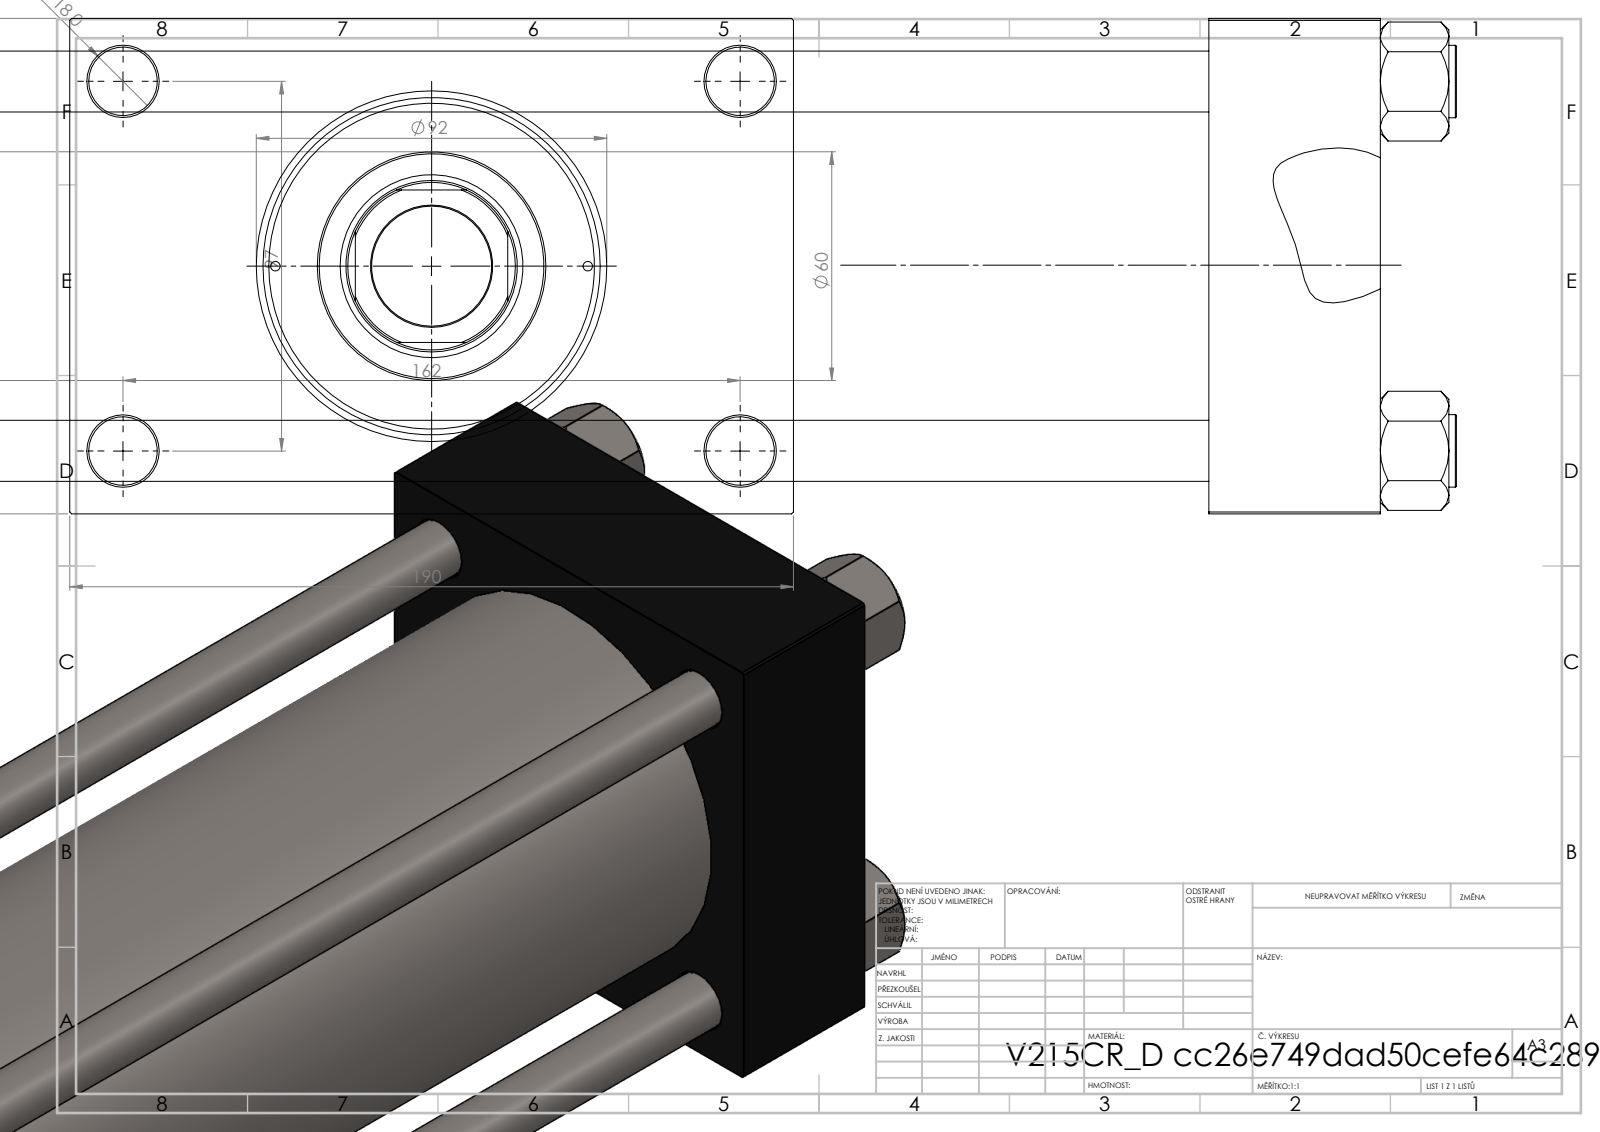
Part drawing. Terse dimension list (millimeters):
name: NUT_M5_D; V215CR_VCP_D; V215CR_D_TYCINKA; V215CR_D_Body (+1 more)
written by: SolidWorks 2019 (CONFIG_CONTROL_DESIGN)
unit: mm
bodies: 11 solids, 1159 faces (547 planar, 92 cylindrical, 520 other)
size: 523 × 190 × 130
volume: 3 532 000 mm³; area: 631 811 mm²
holes: 4× ⌀16, 4× ⌀18, 2× ⌀2.5, 2× ⌀7, 2× ⌀26.44, 2× ⌀35, 1× ⌀31.5, 1× ⌀45, 1× ⌀48, 1× ⌀76, 1× ⌀85.5, 1× ⌀100
bosses: 4× ⌀19, 1× ⌀106, 1× ⌀92, 1× ⌀60
rounds: 1× R22
face distances: 130, 45, 396, 351, 446, 401, 50, 30, 160, 96
hole spacings: 32.55, 49.02, 62.87, 68.52, 94.41, 96.9, 101.73, 102.27
